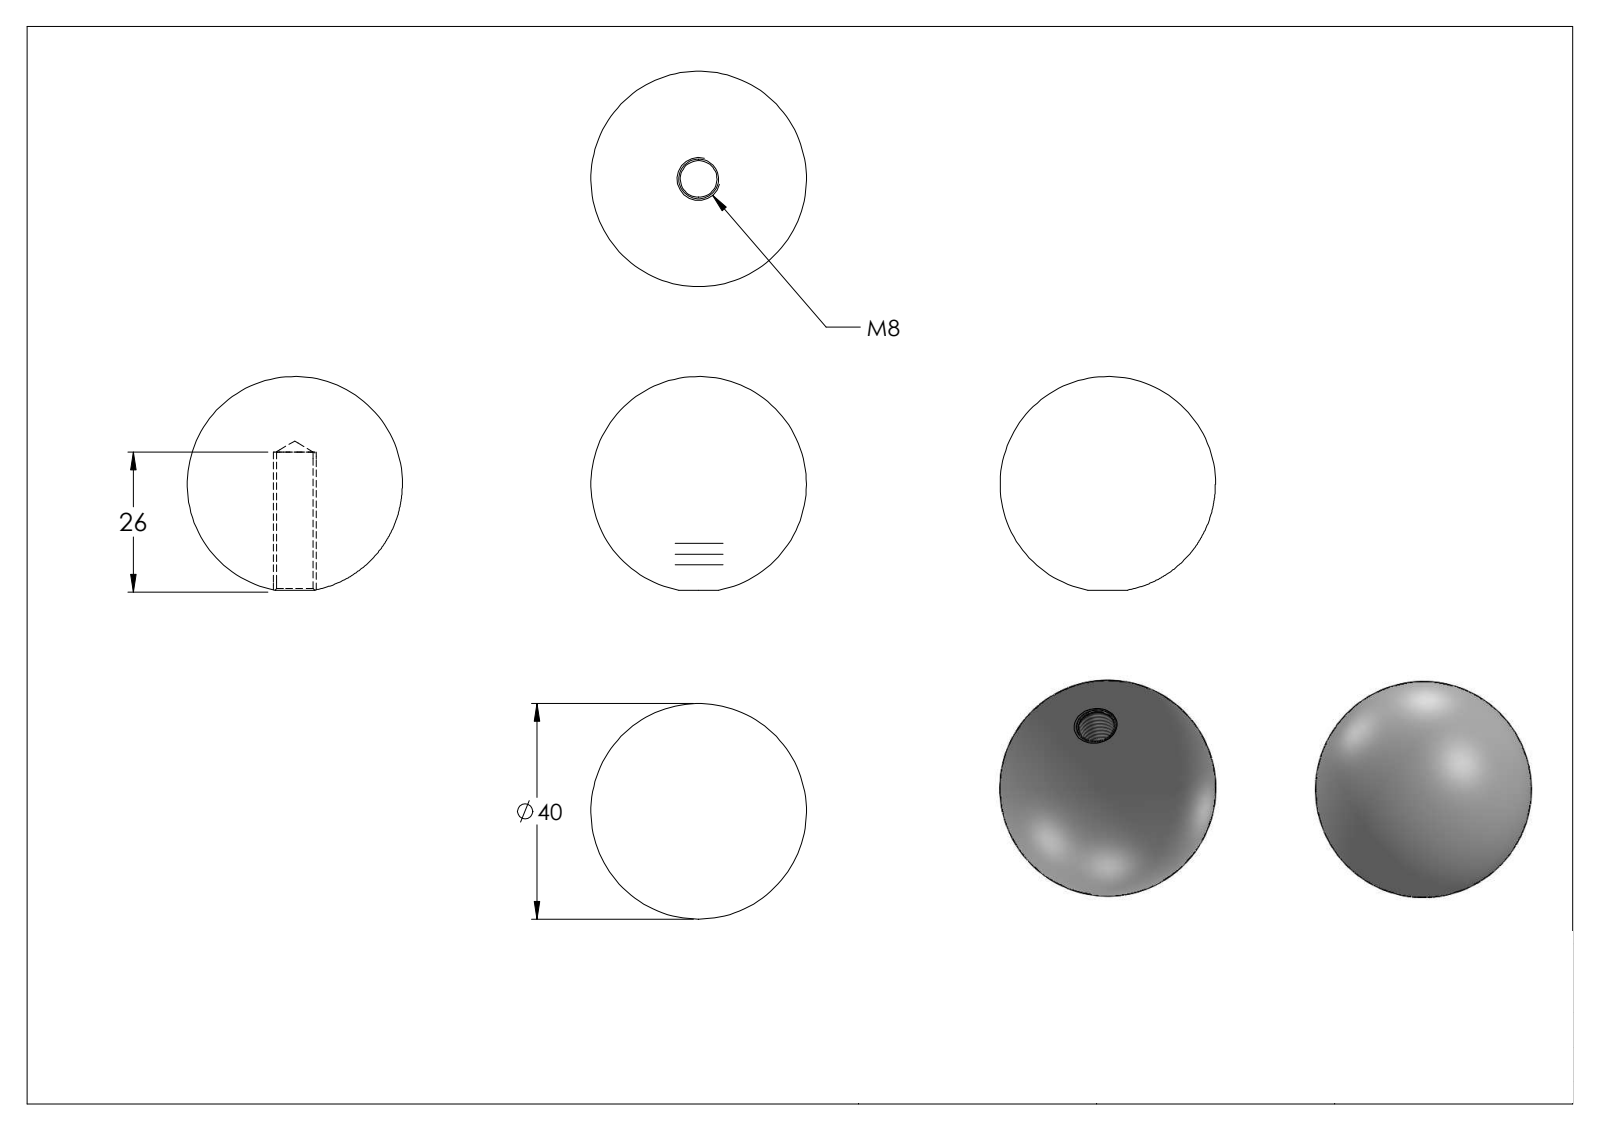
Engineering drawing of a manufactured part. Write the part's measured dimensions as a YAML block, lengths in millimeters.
part_name: "51040-240"
step_written_by: "SolidWorks 2018 (CONFIG_CONTROL_DESIGN)"
units: millimeters
bodies: {solids: 1, faces: 4, planar: 0, cylindrical: 1, other: 3}
overall_size: [40, 40, 39.66]
volume: 32546
surface_area: 5577
round_holes:
  - {diameter: 6.8, count: 1}
